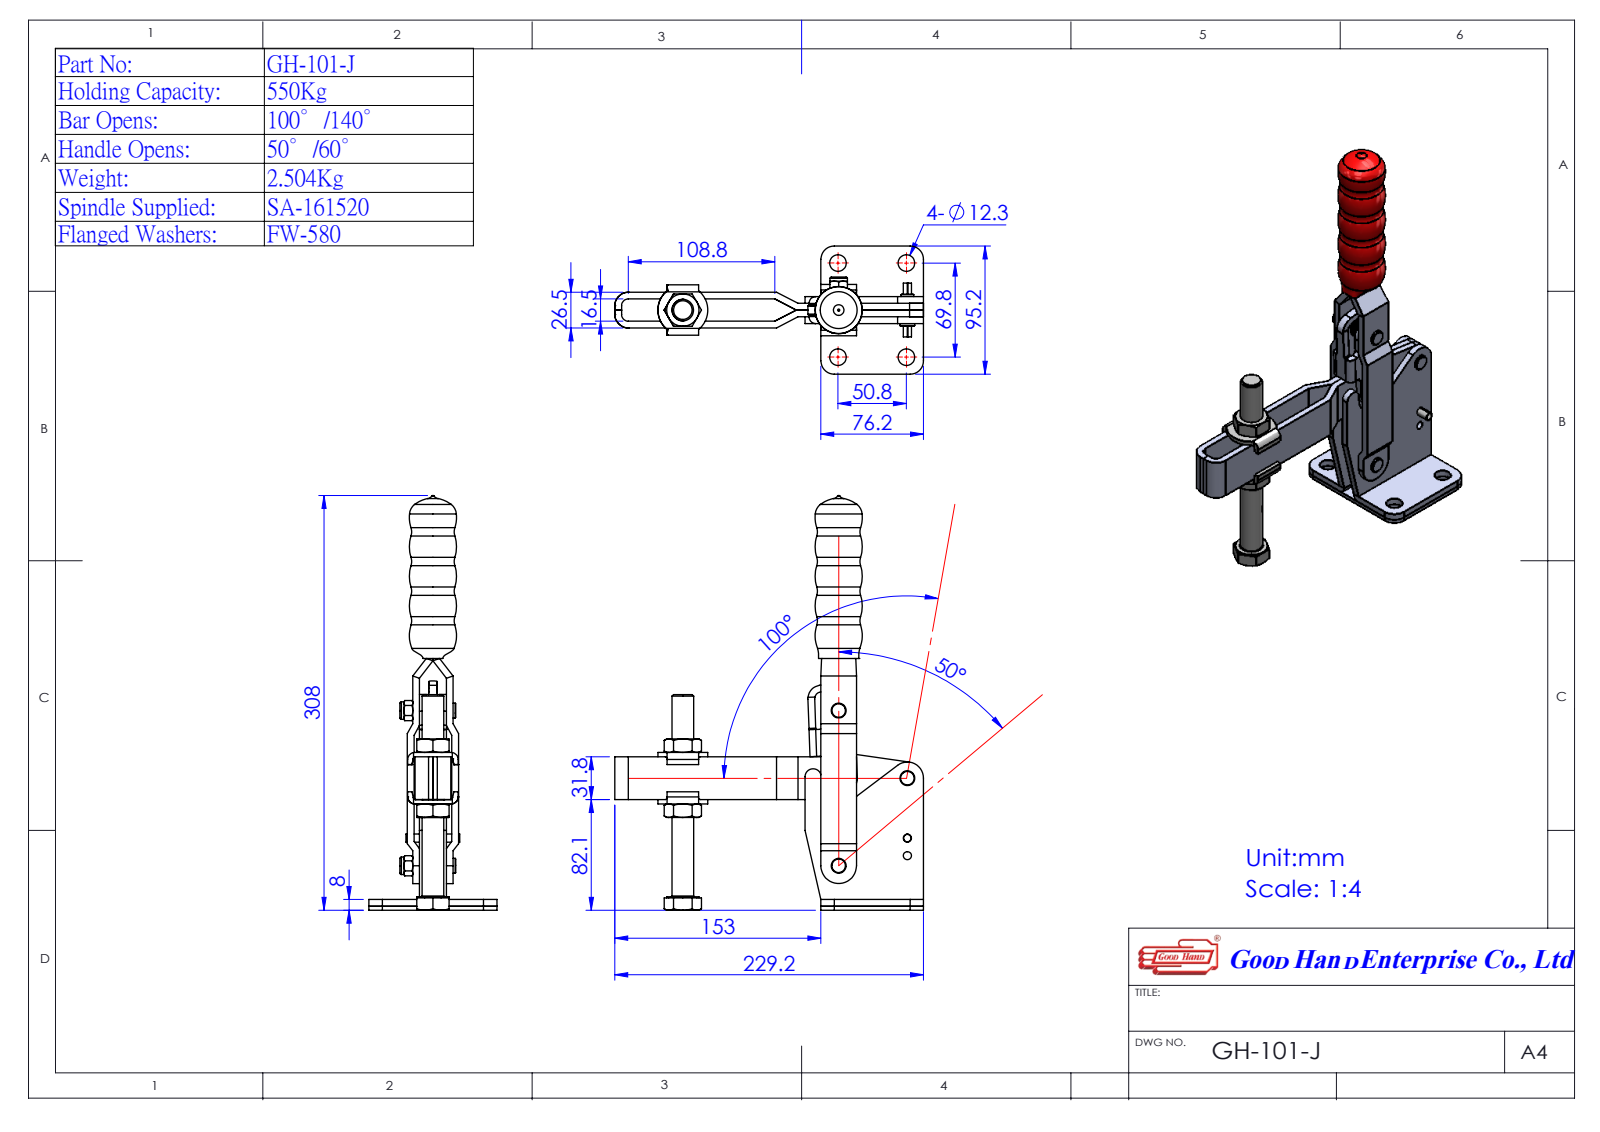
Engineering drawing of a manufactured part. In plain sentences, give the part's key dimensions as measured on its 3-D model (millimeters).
The part is named "Group3^GH-101-J(簡化); Group2^GH-101-J(簡化); Group1^GH-101-J(簡化); GH-101-J(簡化) (+2 more)". Its 3-D file was written by "SolidWorks 2016 (AUTOMOTIVE_DESIGN)". It is 4 solids with 378 faces: 168 planar, 128 cylindrical and 82 other. Overall it measures 307.8 by 229.2 by 95.2 millimeters. Its volume is 265 246 cubic millimeters and its surface area 143 134 square millimeters. Round holes: 5 of diameter 6, 4 of diameter 12.3, 1 of diameter 5.5. Round bosses or shafts: 4 of diameter 11, 2 of diameter 8, 2 of diameter 7.94, 1 of diameter 24, 1 of diameter 16, 1 of diameter 6. Partial cylindrical surfaces (rounded edges, fillets, slot ends): 6 of radius 5, 6 of radius 10, 4 of radius 2, 4 of radius 5.2, 3 of radius 12, 2 of radius 3, 2 of radius 11, 1 of radius 6. The main face-to-face distances are 5, 15, 10, 3.25, 18.25, 20, 23.25, 1.75, 24, 5.75. The hole center spacings are 50.8, 69.8, 86.33, 13, 44.48, 49.25, 50.23, 51.55.
